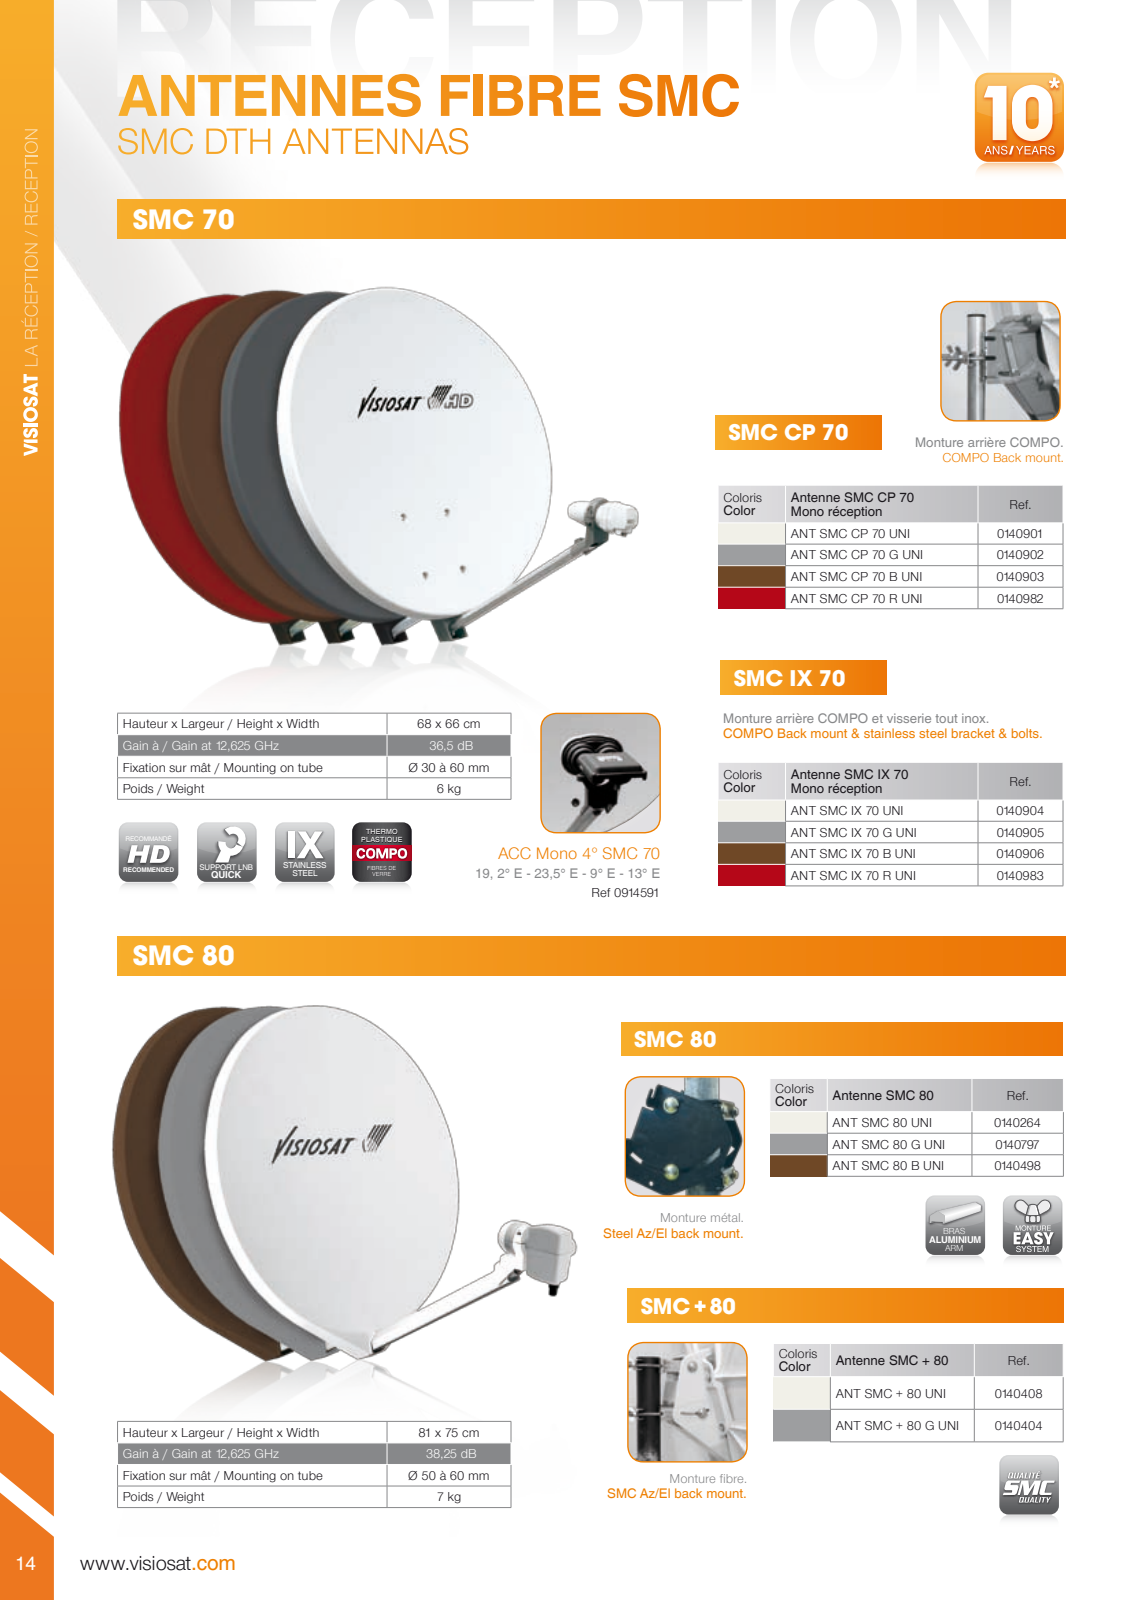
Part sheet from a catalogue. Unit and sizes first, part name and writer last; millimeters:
Units: millimetres
Overall size (bounding box): 74.6 × 9.6 × 9.6
Round holes (diameter × count): ⌀6.7 ×1
Round bosses / shafts (diameter × count): ⌀9.6 ×1, ⌀9.53 ×1, ⌀7.55 ×1
Main face-to-face distances: 61.9, 12.7, 74.6
Volume: 4 748 mm³ · Surface area: 2 873 mm²
Bodies: 2 solids, 26 faces (4 planar, 10 cylindrical, 12 other)
STEP written by: ACIS (automotive_design)
